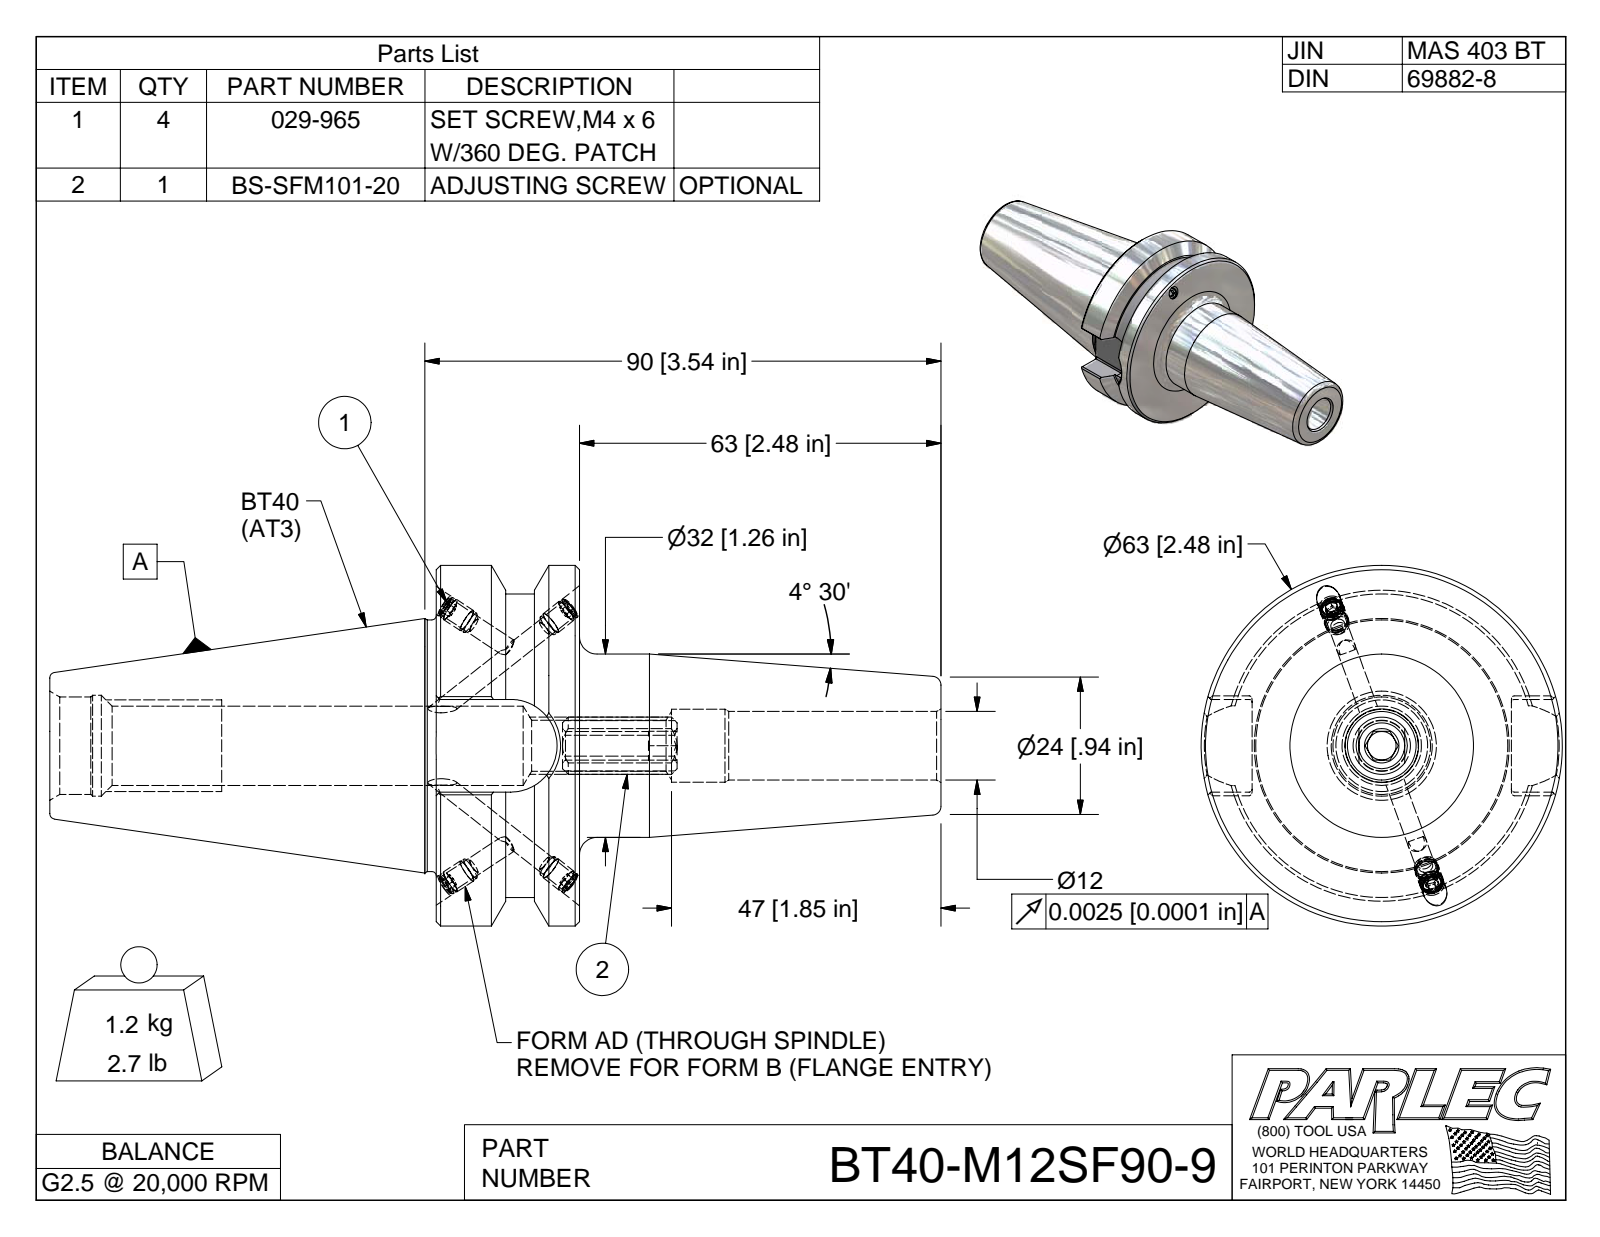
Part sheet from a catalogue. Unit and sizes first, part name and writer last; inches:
Units: inches
Overall size (bounding box): 6.118 × 2.48 × 2.48
Round holes (diameter × count): ⌀0.13 ×4, ⌀0.161 ×4, ⌀0.471 ×1, ⌀0.501 ×1, ⌀0.694 ×1
Round bosses / shafts (diameter × count): ⌀0.165 ×4, ⌀0.157 ×4, ⌀2.48 ×1, ⌀2.087 ×1, ⌀1.75 ×1, ⌀1.73 ×1, ⌀1.26 ×1
Partial cylindrical surfaces — rounded edges, fillets, slot ends (radius × count): R0.02 ×8, R0.197 ×1, R0.319 ×1
Main face-to-face distances: 0.984, 1.78, 0.733, 1.048, 3.465, 2.481, 2.653, 3.637, 6.119, 0.637
Volume: 9.497 in³ · Surface area: 49.65 in²
Bodies: 6 solids, 173 faces (79 planar, 43 cylindrical, 51 other)
Part name (STEP PRODUCT): BT40-M12SF90-9; BT40BC-M12SF90-9-1; 029-965; BS-SFM101-20
STEP written by: Autodesk Inventor 2009 (AUTOMOTIVE_DESIGN)
